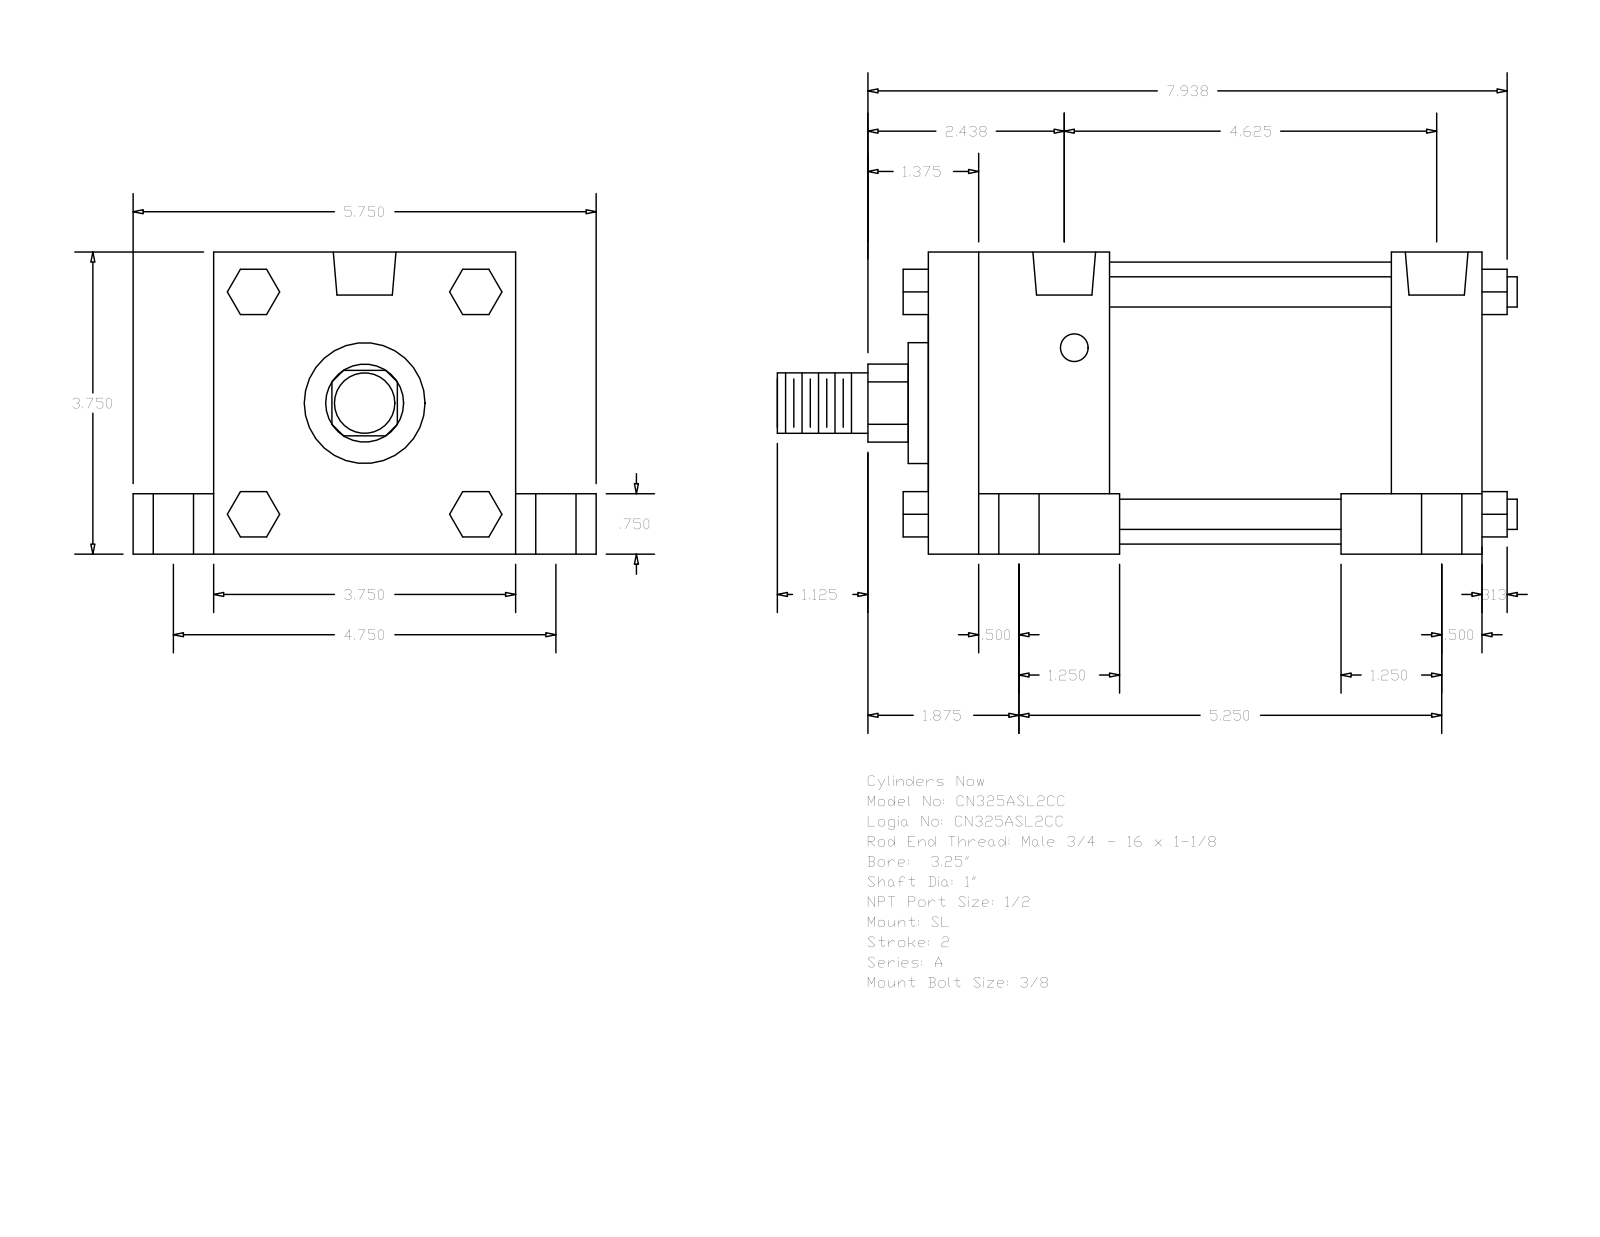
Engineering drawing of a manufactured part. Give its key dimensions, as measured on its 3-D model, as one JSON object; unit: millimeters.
{"part_name": "A_SL__0325_1", "step_written_by": "GSSL Pune (CONFIG_CONTROL_DESIGN)", "units": "millimeters", "bodies": {"solids": 0, "faces": 150, "planar": 114, "cylindrical": 36, "other": 0}, "overall_size": [233.36, 146.05, 95.25], "round_holes": [[8.73, 4], [12.7, 4], [19.05, 4], [19.77, 2]], "round_bosses_or_shafts": [[9.53, 4], [88.9, 1], [38.1, 1], [25.4, 1], [19.05, 1]], "partial_cylinders_radius": [[12.29, 1]], "face_to_face_distances": [95.24, 174.63, 19.05, 25.41, 120.65, 76.19, 57.15, 146.05, 88.9, 117.48], "hole_center_spacings": [3.18, 60.35, 60.52, 62, 62.81, 111.12, 114.3, 120.66]}
